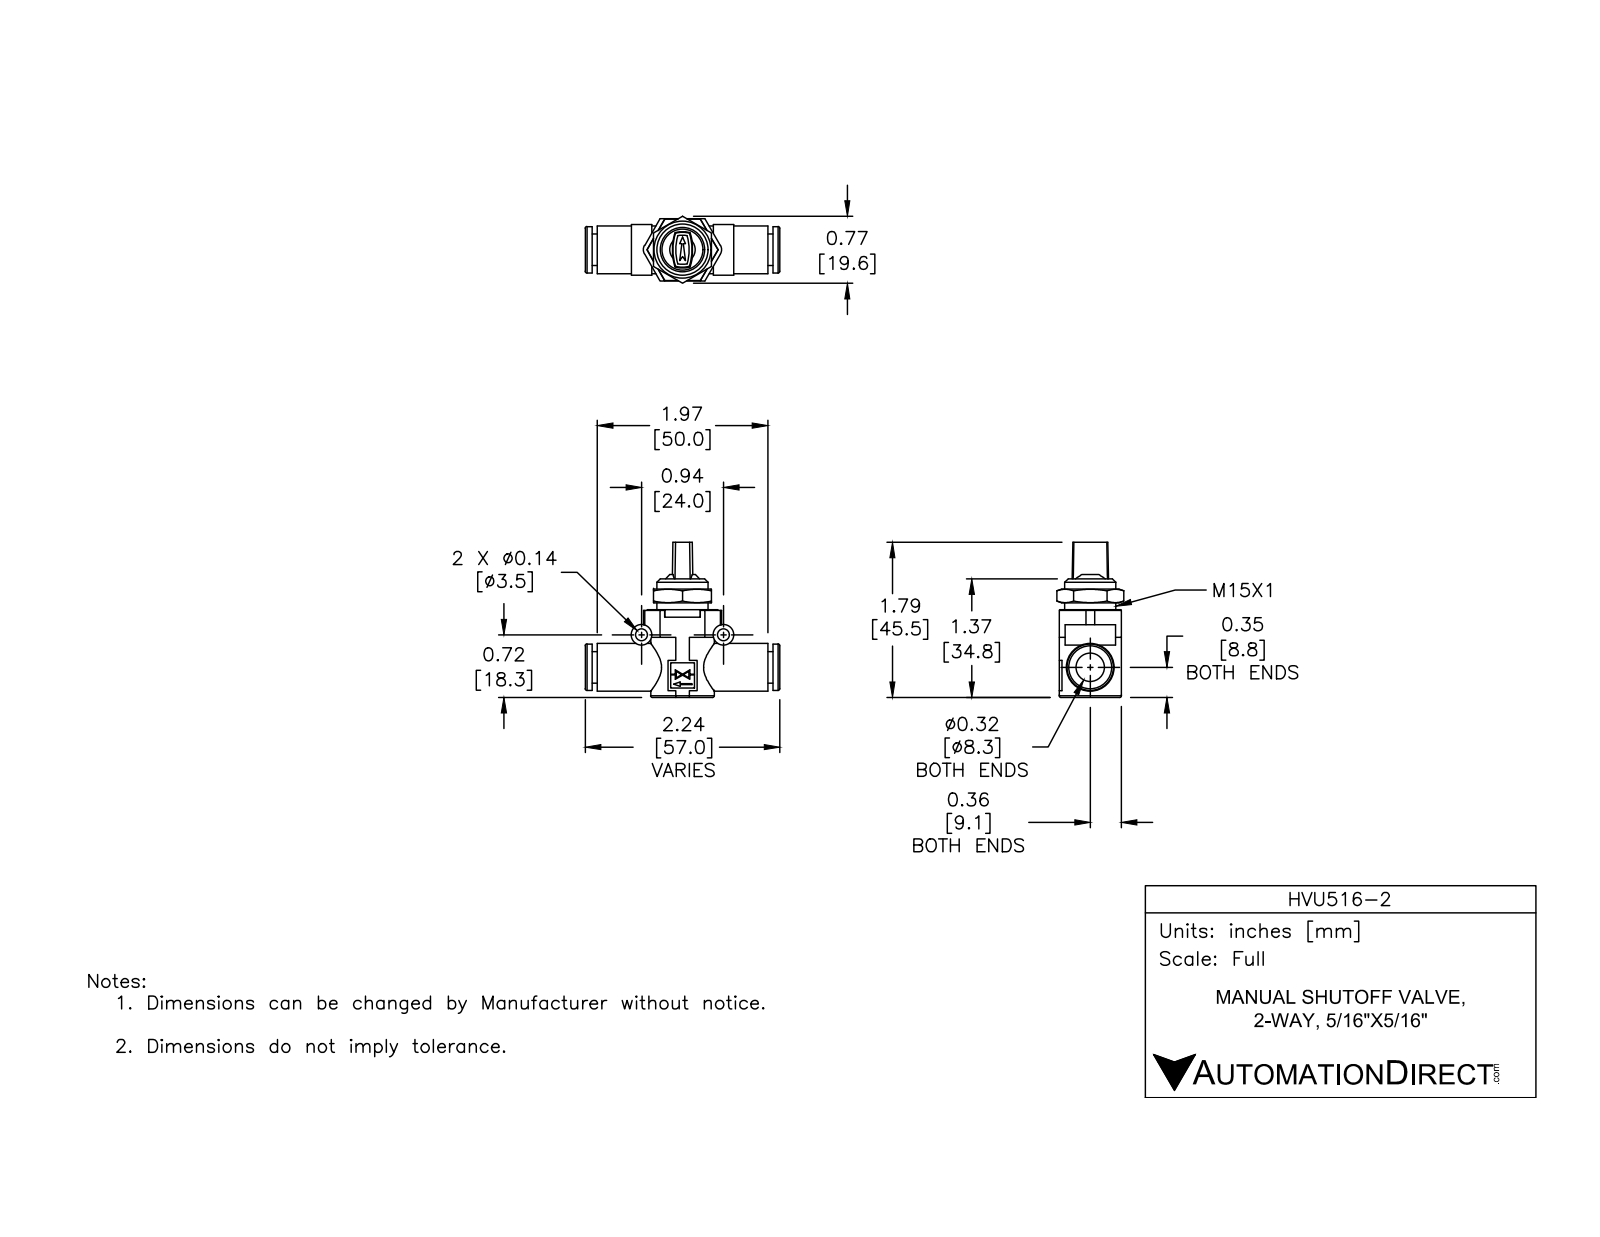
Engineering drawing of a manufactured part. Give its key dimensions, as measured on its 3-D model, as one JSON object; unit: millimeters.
{"part_name": "HVU516-2", "step_written_by": "SolidWorks 2015 (CONFIG_CONTROL_DESIGN)", "units": "millimeters", "bodies": {"solids": 4, "faces": 172, "planar": 105, "cylindrical": 47, "other": 20}, "overall_size": [57, 45.5, 19.63], "volume_mm3": 13788, "surface_area_mm2": 8787, "round_holes": [[3.5, 2], [8.25, 1], [9.5, 1], [12, 1]], "round_bosses_or_shafts": [[6, 2], [18.65, 1], [15, 1], [14, 1], [13.55, 1], [9.25, 1]], "partial_cylinders_radius": [[0.5, 2], [2.5, 2], [7.03, 2], [14.56, 2]], "face_to_face_distances": [23.49, 2, 1.5, 51.5, 18, 3.5, 53.5, 55, 18.22, 20.5], "hole_center_spacings": [24]}
